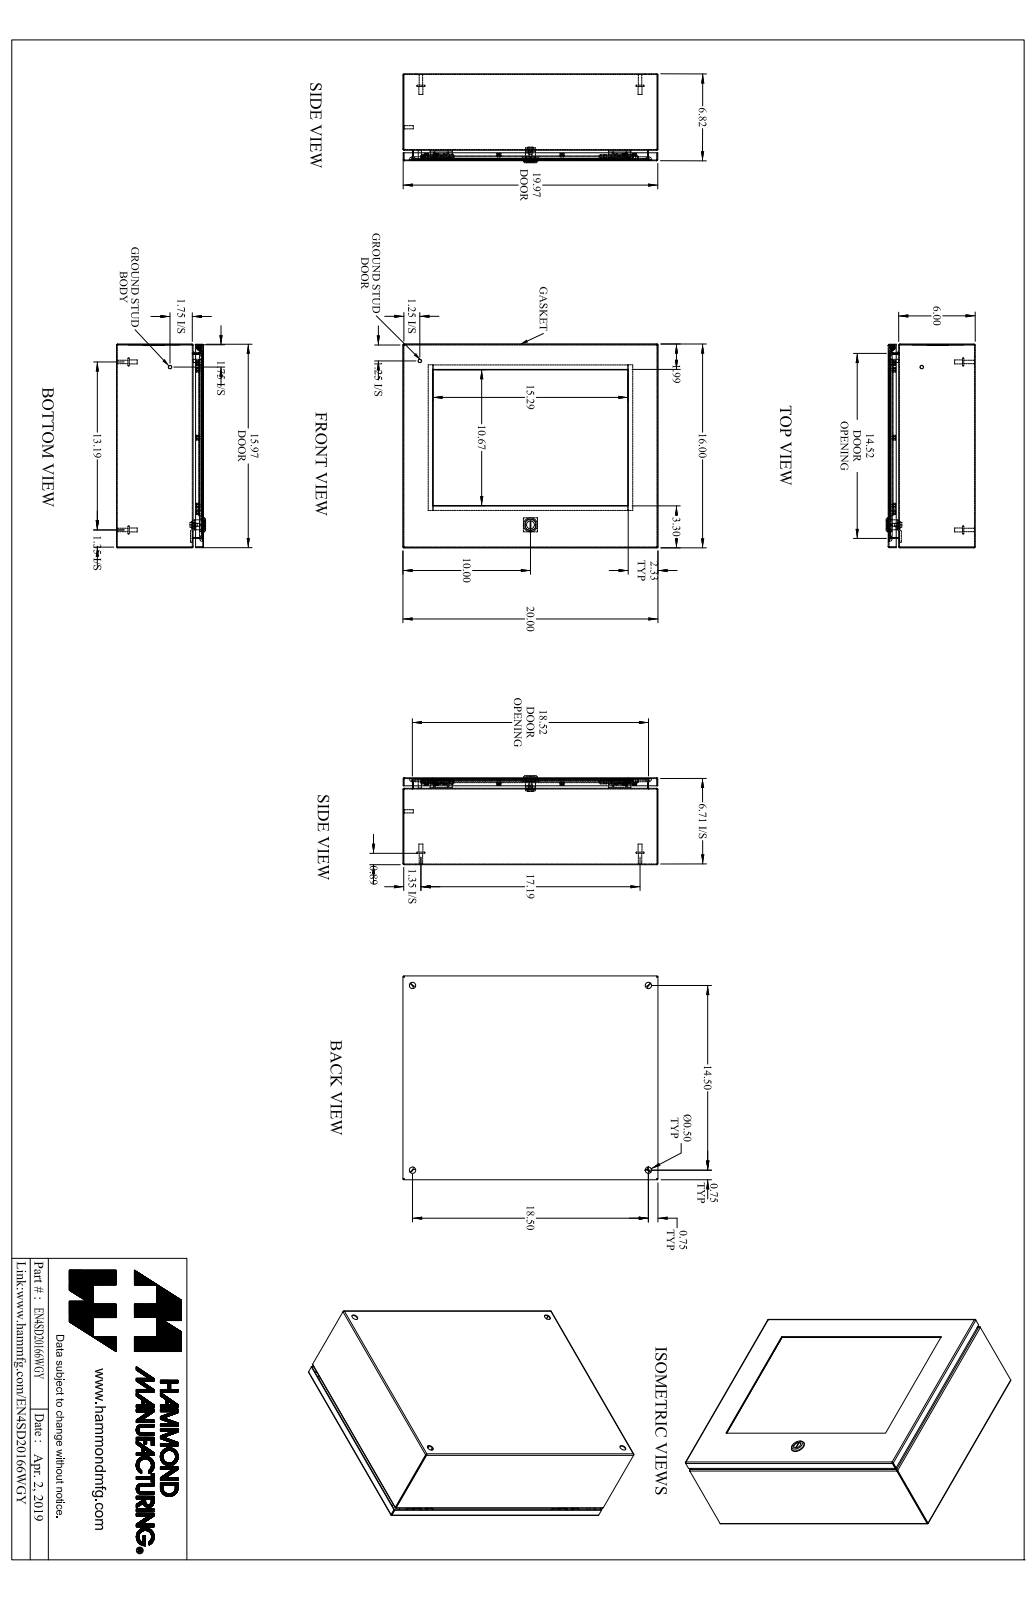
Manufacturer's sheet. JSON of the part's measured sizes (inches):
{"part_name": "EN4SD20166WGY_Default", "step_written_by": "SolidWorks 2019 (CONFIG_CONTROL_DESIGN)", "units": "inches", "bodies": {"solids": 58, "faces": 1197, "planar": 594, "cylindrical": 369, "other": 234}, "overall_size": [20, 16, 6.982], "volume_in3": 116.3, "surface_area_in2": 2803, "round_holes": [[0.13, 14], [0.25, 14], [0.5, 4], [0.172, 1], [0.232, 1], [0.24, 1], [0.242, 1], [0.625, 1], [0.785, 1]], "round_bosses_or_shafts": [[0.226, 15], [0.368, 14], [0.164, 14], [0.625, 4], [0.313, 4], [0.27, 4], [0.281, 2], [0.25, 2]], "partial_cylinders_radius": [[0.029, 21], [0.086, 21], [0.25, 16], [0.125, 10], [19, 8], [0.006, 4], [0.016, 4], [0.062, 4]], "face_to_face_distances": [0.057, 6.765, 6.708, 15.943, 0.25, 6.458, 6.515, 19.943, 0.307, 6.822], "hole_center_spacings": [4.958, 15.612, 15.614, 5.335, 9.917, 12.551, 12.714, 12.716]}
